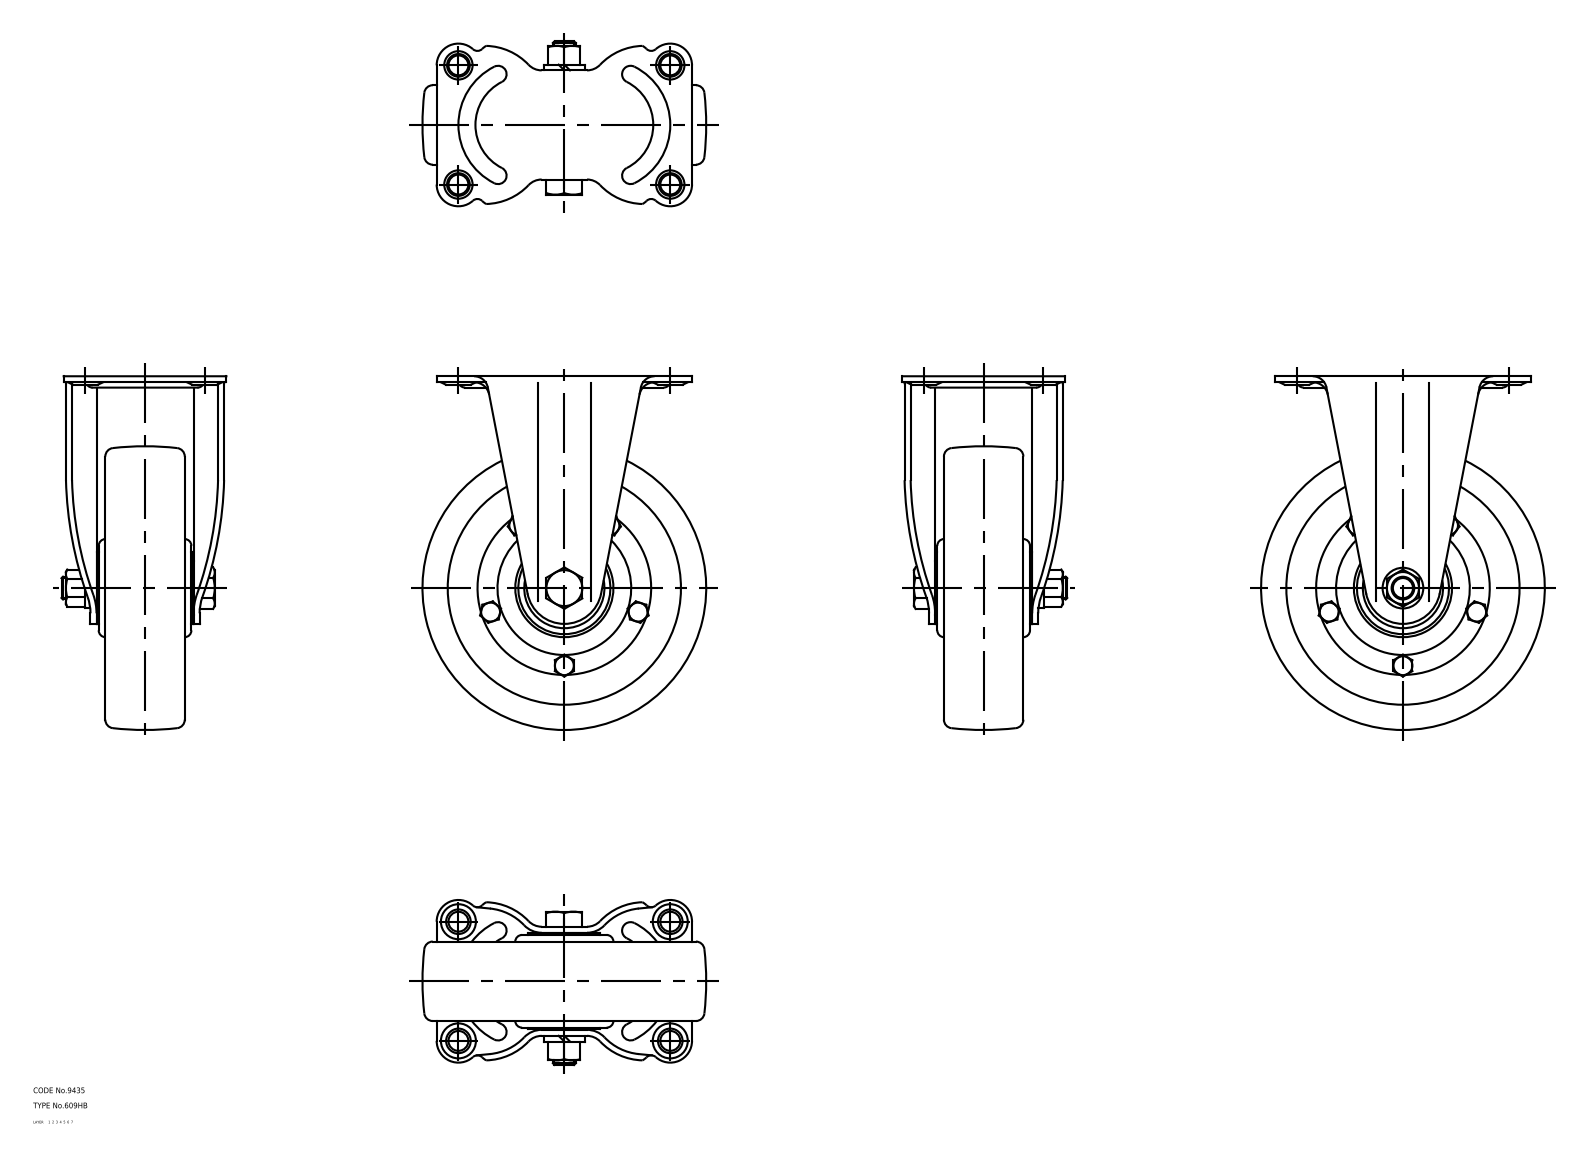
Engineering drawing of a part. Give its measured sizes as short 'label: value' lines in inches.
name: 67130240; 67130253; 67130266
written by: CADfix (AUTOMOTIVE_DESIGN)
unit: in
bodies: 3 solids, 348 faces (0 planar, 0 cylindrical, 348 other)
size: 7.362 × 5.906 × 3.431
volume: 45.64 in³; area: 182.5 in²
